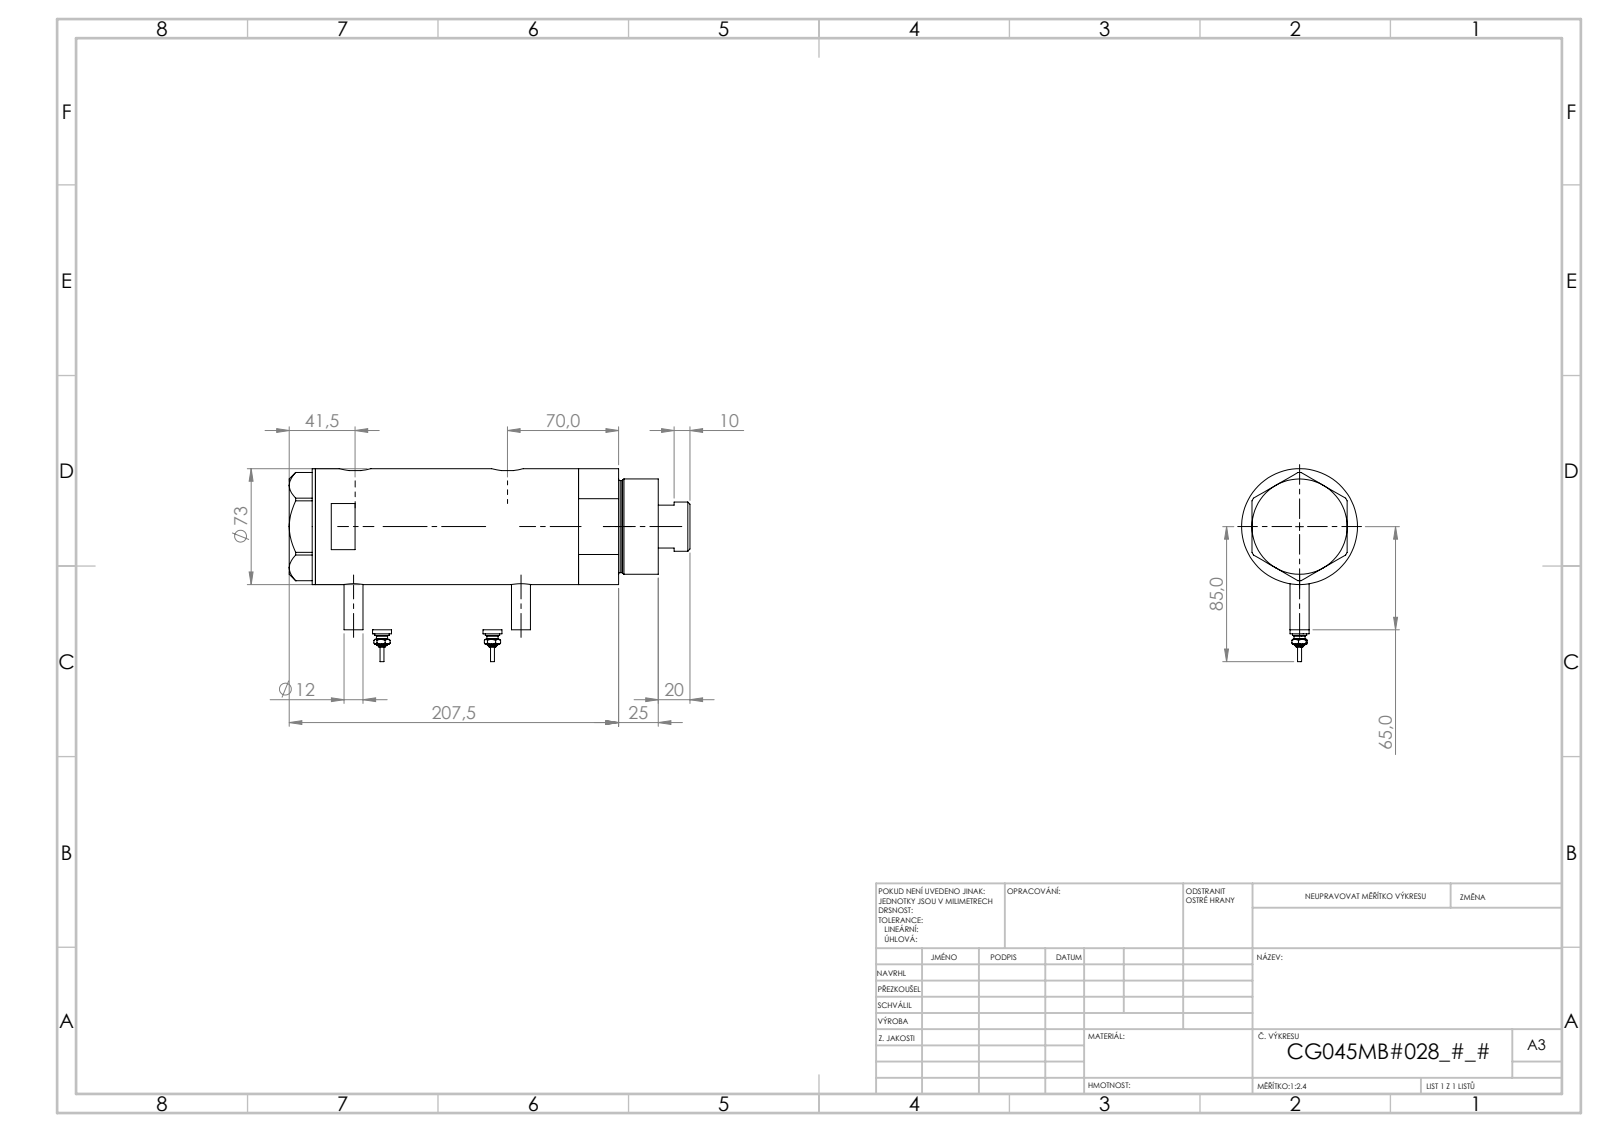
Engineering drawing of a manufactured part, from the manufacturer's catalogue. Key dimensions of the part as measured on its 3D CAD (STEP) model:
Part name (STEP PRODUCT): V270CG_FRONT; V270CG_MIDDLE; Switch; V270CG_BACK (+1 more)
STEP written by: SolidWorks 2019 (CONFIG_CONTROL_DESIGN)
Units: millimetres
Bodies: 6 solids, 212 faces (77 planar, 71 cylindrical, 64 other)
Overall size (bounding box): 252.5 × 121.5 × 73
Volume: 909 455 mm³ · Surface area: 152 628 mm²
Round holes (diameter × count): ⌀12.5 ×2, ⌀13.16 ×2, ⌀10.5 ×1, ⌀32 ×1, ⌀33.5 ×1, ⌀45 ×1, ⌀48 ×1, ⌀64 ×1
Round bosses / shafts (diameter × count): ⌀12 ×4, ⌀9 ×2, ⌀7 ×2, ⌀4.5 ×2, ⌀2.5 ×2, ⌀73 ×1, ⌀60 ×1, ⌀58 ×1
Partial cylindrical surfaces — rounded edges, fillets, slot ends (radius × count): R10 ×2
Main face-to-face distances: 95, 121, 26, 16.5, 42.5, 137.5, 2, 216, 28, 123
Hole centre spacings: 1, 8.5, 96, 97, 104.5, 105.5
